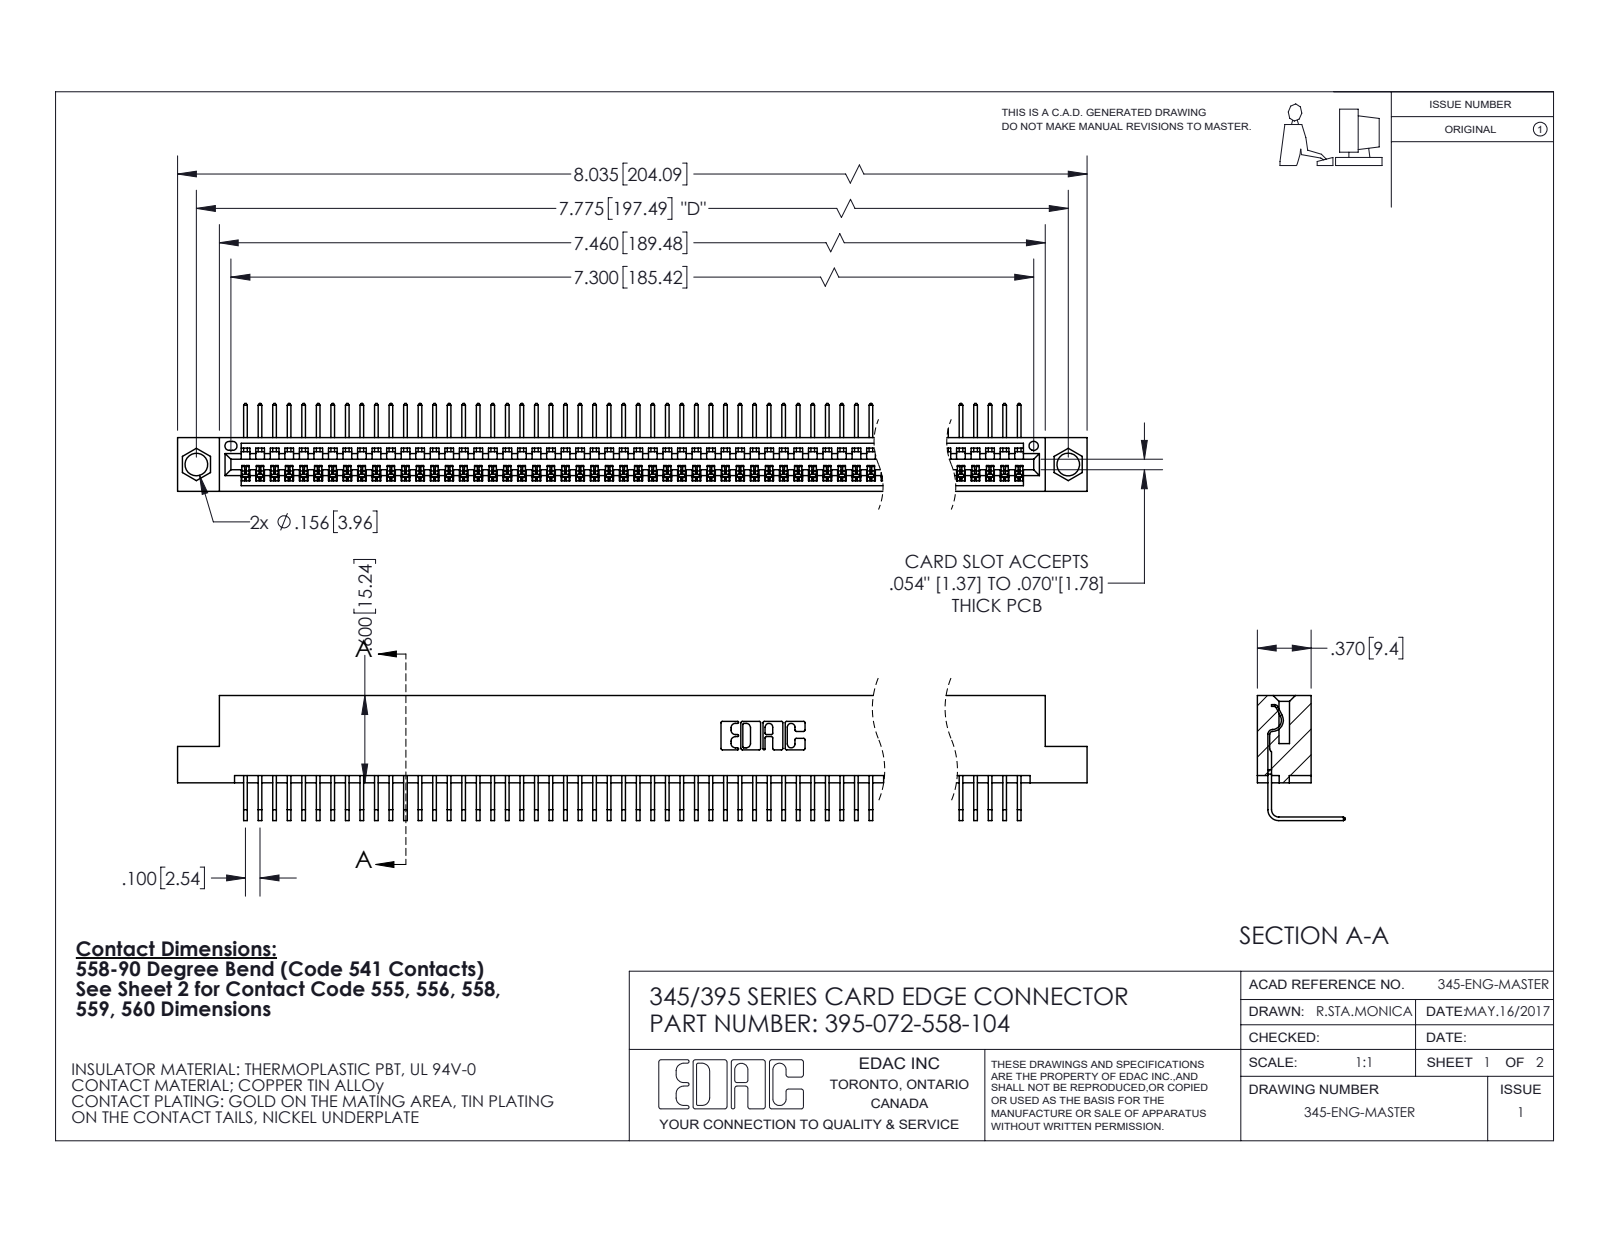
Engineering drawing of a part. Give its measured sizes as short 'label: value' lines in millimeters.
name: 395-072-558-104; 345 Part_Flush Mounting Lugs - 0.156 Dia-TI; 345-292-001_558 Tail - 2
written by: SolidWorks 2020 (CONFIG_CONTROL_DESIGN)
unit: mm
bodies: 73 solids, 4460 faces (3118 planar, 1342 cylindrical, 0 other)
size: 204.1 × 21.8 × 15.4
volume: 19 760 mm³; area: 27 920 mm²
holes: 2× ⌀4, 1× ⌀1.6
rounds: 144× R0.2, 22× R0.3, 6× R0.2, 6× R0.8, 3× R0.7, 2× R0.8, 2× R1, 1× R0.4
face distances: 1.8, 7.6, 9.4, 5.1, 2.5, 6.9, 0.6, 5.7, 3.8, 1.8
hole spacings: 6.9, 191.5, 197.5
